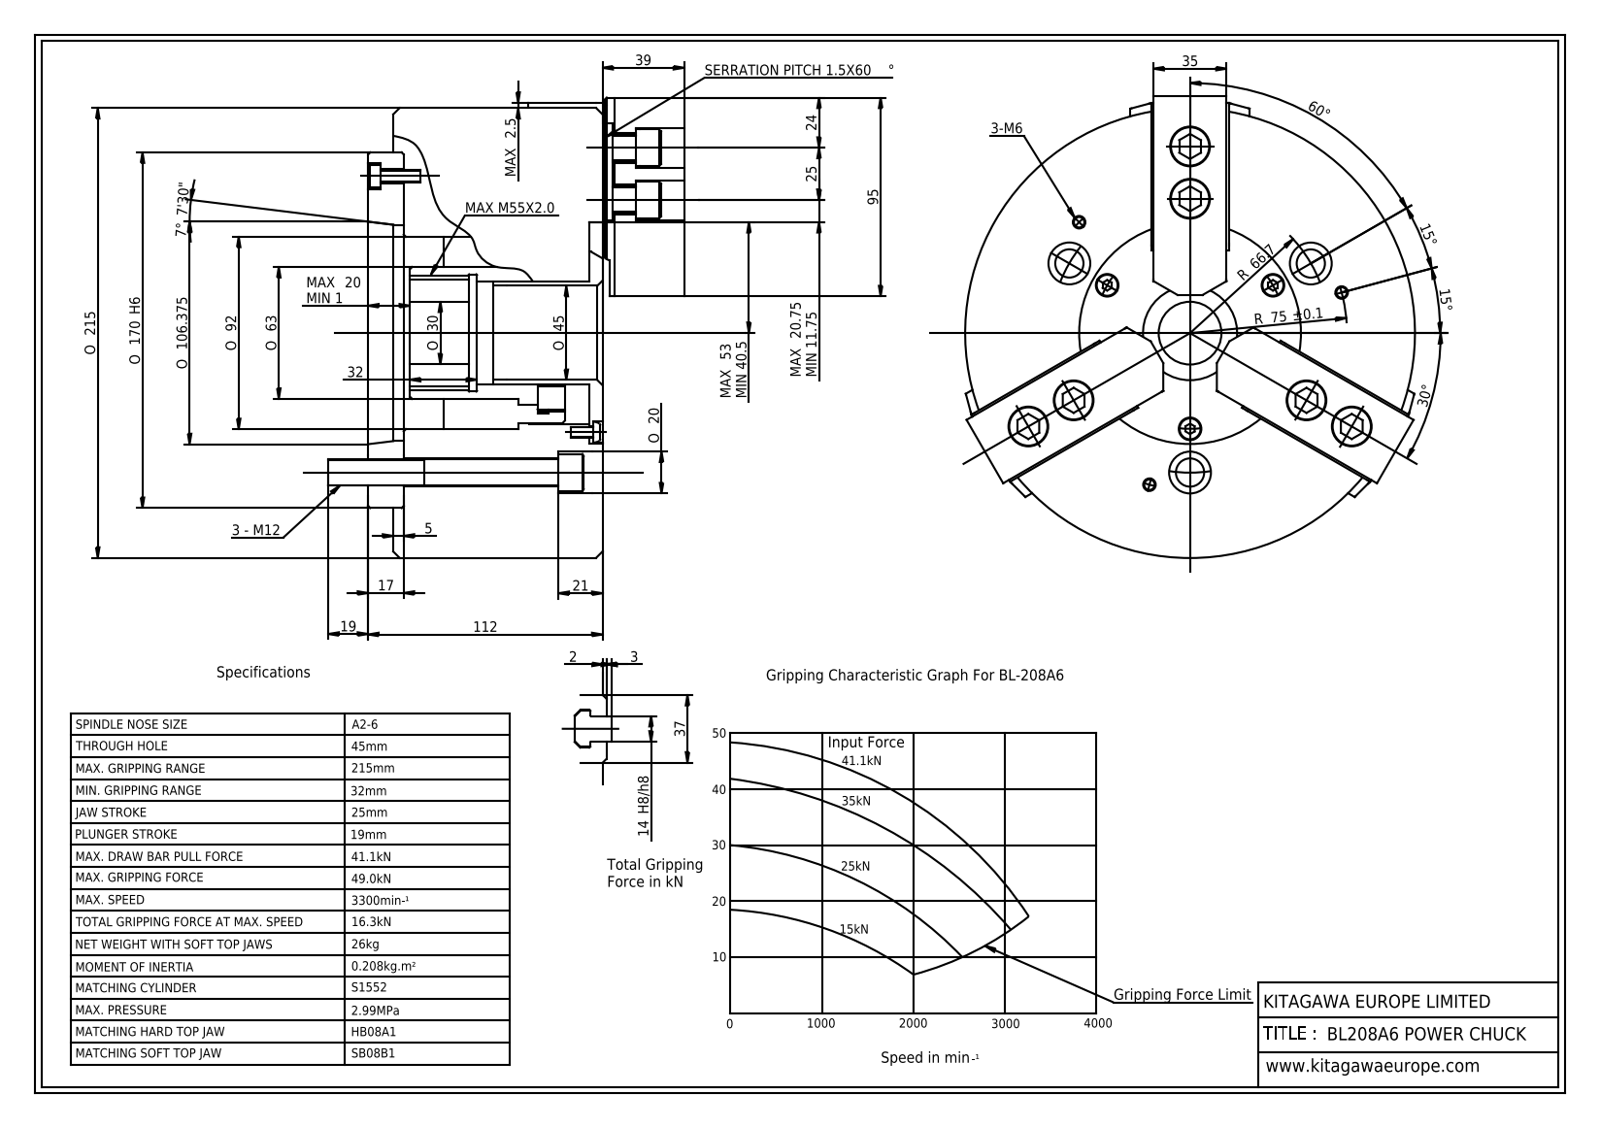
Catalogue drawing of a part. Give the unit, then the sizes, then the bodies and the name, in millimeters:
Units: millimetres
Overall size (bounding box): 230.27 × 229.54 × 151.2
Round holes (diameter × count): ⌀14 ×9, ⌀6 ×8, ⌀8 ×8, ⌀5 ×7, ⌀6.8 ×6, ⌀9 ×6, ⌀12 ×6, ⌀13 ×6, ⌀13.5 ×6, ⌀19 ×6, ⌀11 ×5, ⌀4.2 ×3
Round bosses / shafts (diameter × count): ⌀18 ×6, ⌀13 ×6, ⌀19 ×3, ⌀9.5 ×3, ⌀6.8 ×2, ⌀215 ×1
Partial cylindrical surfaces — rounded edges, fillets, slot ends (radius × count): R6 ×12, R7.5 ×12, R10 ×12, R10.5 ×9, R0.4 ×6, R1 ×3, R2 ×3, R3.6 ×3
Main face-to-face distances: 95, 5, 17, 12, 28, 36, 62, 67, 33, 7
Hole centre spacings: 66.67, 20.25, 115.48, 29.78, 36.21, 54.83, 64.17, 75
Volume: 3 543 000 mm³ · Surface area: 605 788 mm²
Bodies: 42 solids, 2821 faces (2419 planar, 274 cylindrical, 128 other)
Part name (STEP PRODUCT): BL208A6_ASSY
STEP written by: ST-DEVELOPER v16.7 (AUTOMOTIVE_DESIGN)
